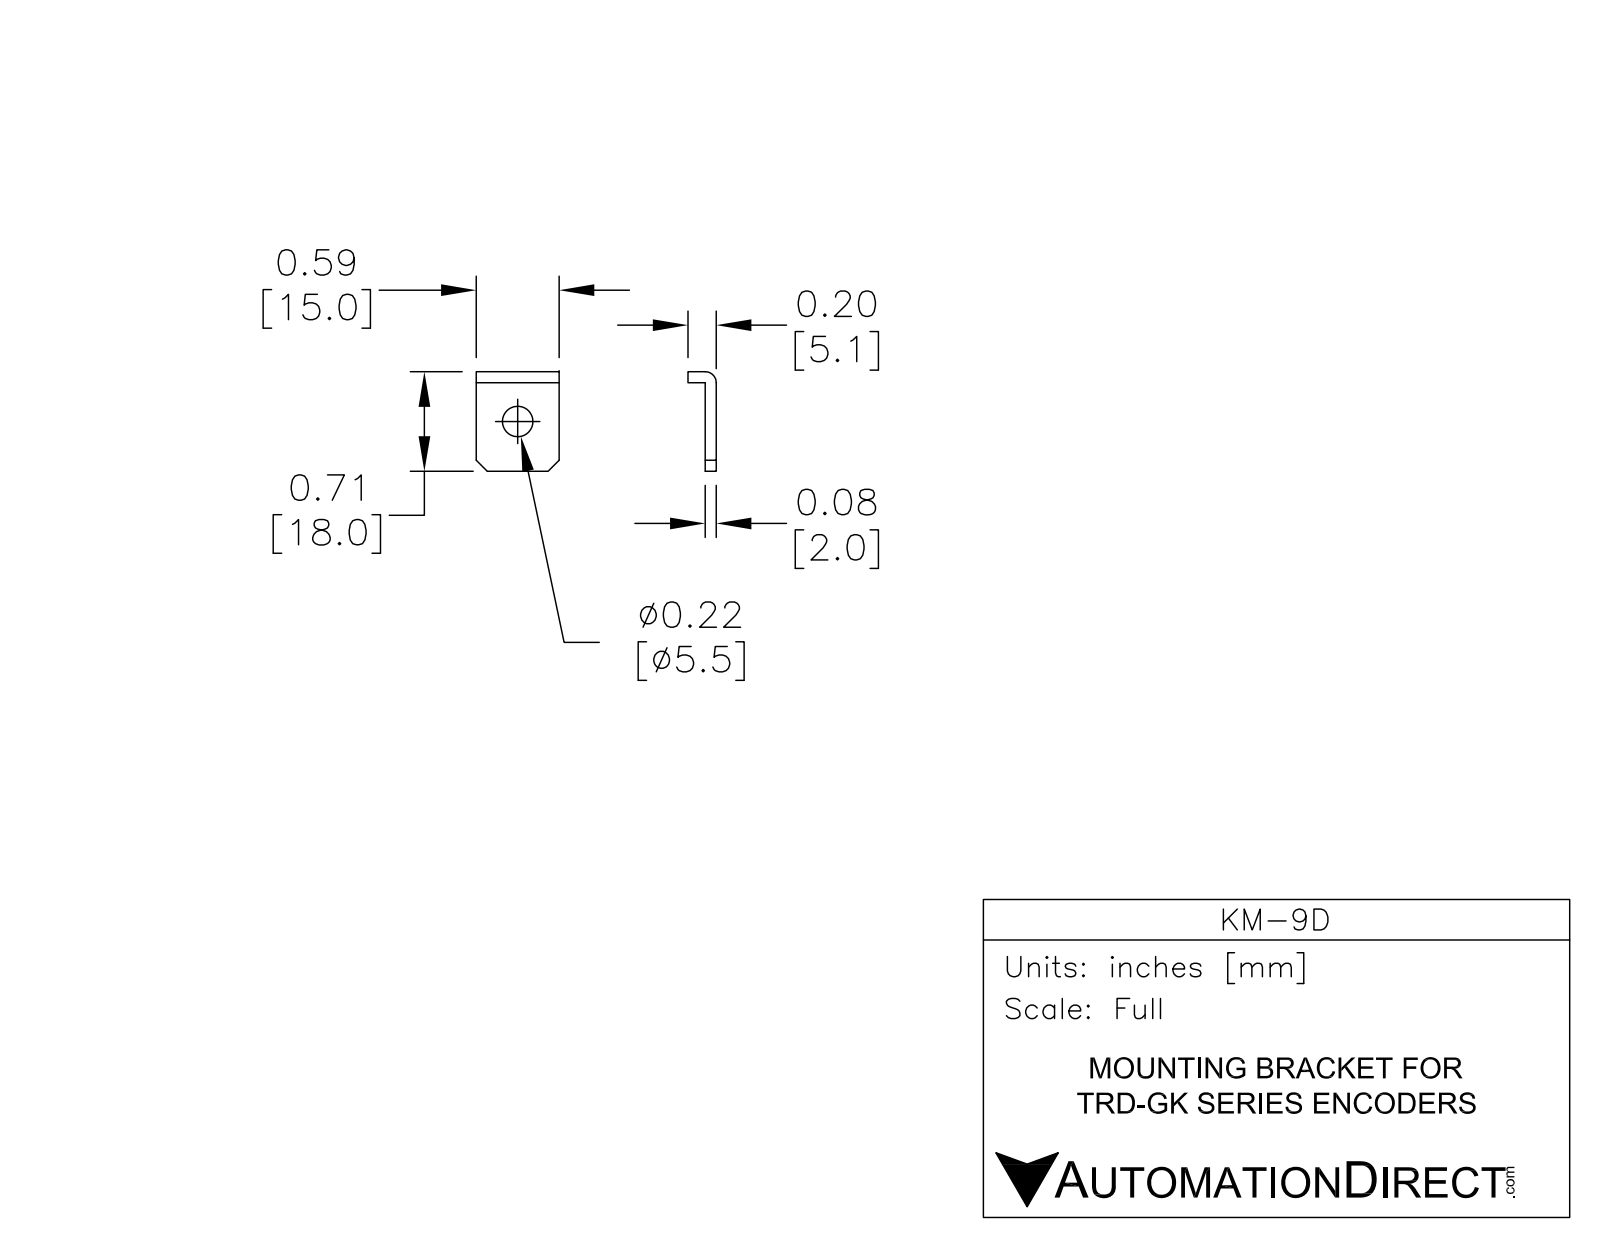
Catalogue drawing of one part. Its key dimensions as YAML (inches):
part_name: "KM-9"
step_written_by: "PRO/ENGINEER BY PARAMETRIC TECHNOLOGY CORPORATION, 2010020 (AUTOMOTIVE_DESIGN_CC2)"
units: inches
bodies: {solids: 1, faces: 13, planar: 10, cylindrical: 3, other: 0}
overall_size: [0.709, 0.591, 0.201]
volume: 0.034
surface_area: 1.14
round_holes:
  - {diameter: 0.217, count: 1}
partial_cylinders:
  - {radius: 0.079, count: 1}
face_to_face_distances: [0.079, 0.591, 0.122, 0.201, 0.709, 0.63]
